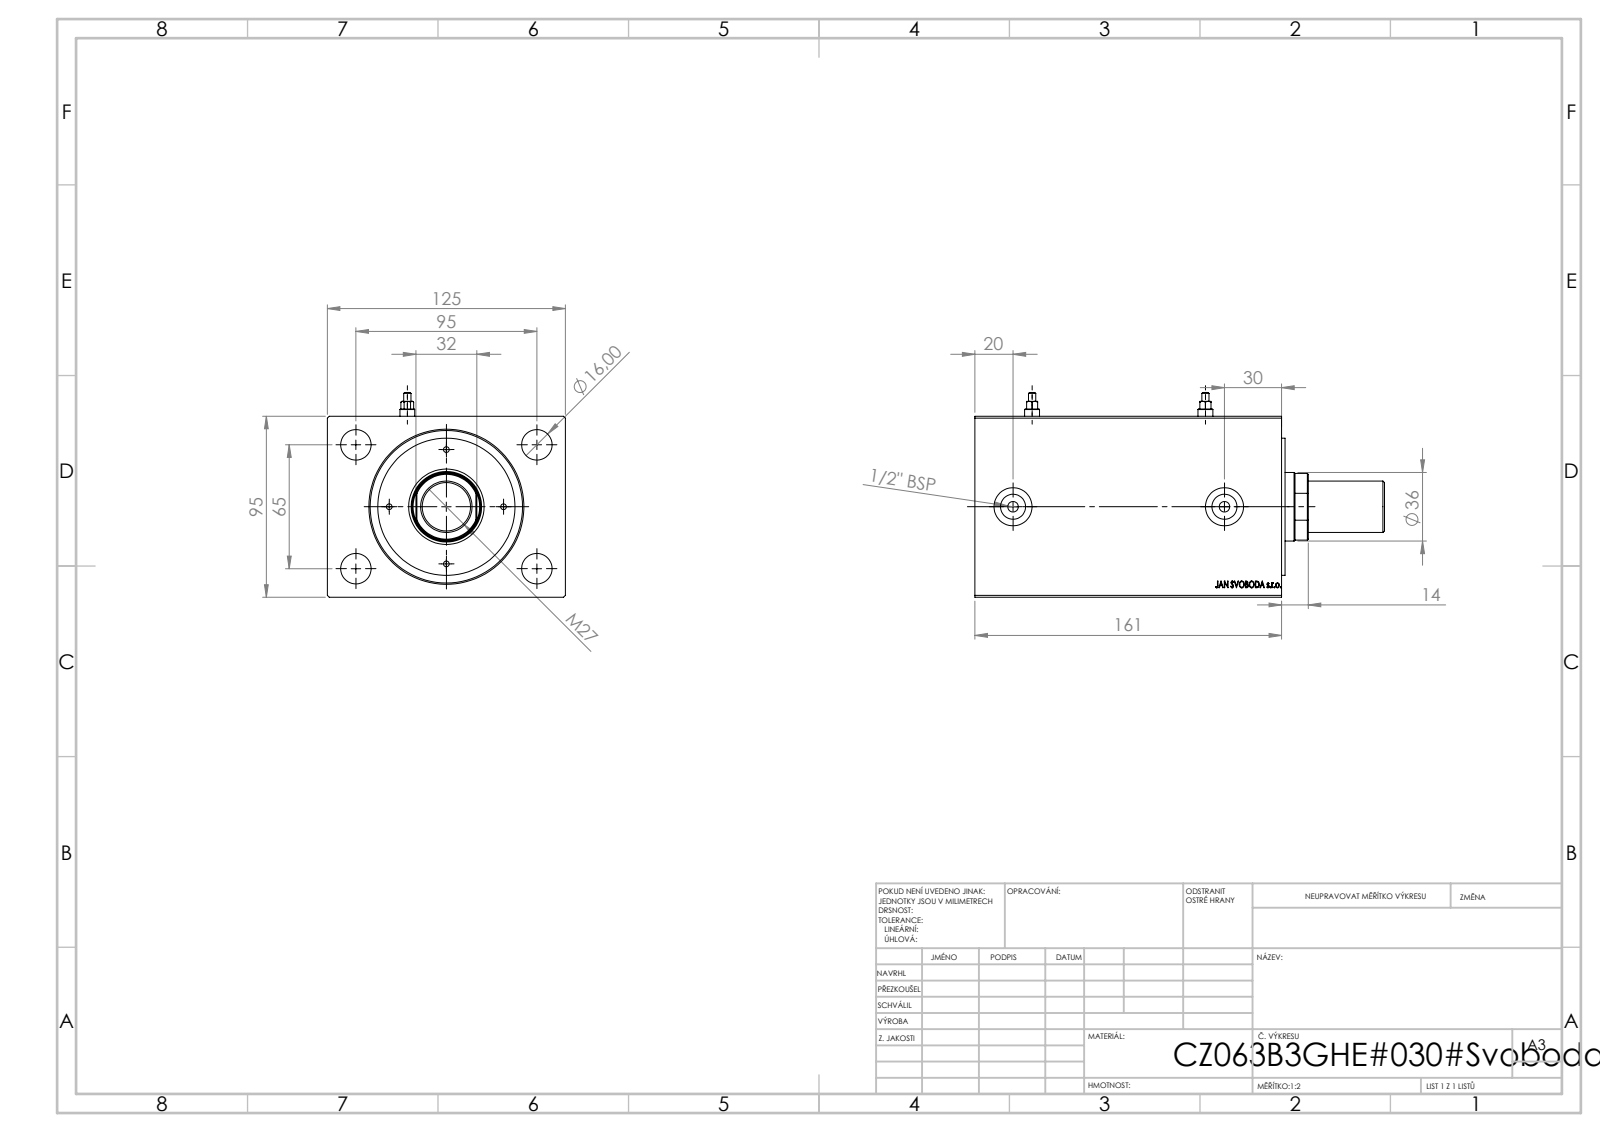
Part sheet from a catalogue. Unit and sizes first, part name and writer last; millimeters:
Units: millimetres
Overall size (bounding box): 215 × 125 × 107.5
Round holes (diameter × count): ⌀3 ×4, ⌀16 ×4, ⌀1.8 ×2, ⌀5.5 ×2, ⌀8 ×2, ⌀13.16 ×2, ⌀20 ×2, ⌀25.5 ×1, ⌀36 ×1, ⌀37 ×1, ⌀63 ×1, ⌀80 ×1
Round bosses / shafts (diameter × count): ⌀7.8 ×2, ⌀3.8 ×2, ⌀72 ×1, ⌀27 ×1
Partial cylindrical surfaces — rounded edges, fillets, slot ends (radius × count): R17.5 ×1
Main face-to-face distances: 95, 125, 161, 140.2, 20.8, 14, 12.2, 1.8, 128, 148.8
Hole centre spacings: 30, 36.91, 42.43, 47.57, 57.55, 78.5, 84.04, 60
Volume: 1 813 000 mm³ · Surface area: 187 755 mm²
Bodies: 6 solids, 940 faces (426 planar, 76 cylindrical, 438 other)
Part name (STEP PRODUCT): V500CZ_SMALL_MALE_METRIC; Zatka_Cushioning3; V500CZ; V500CZ_B_VC
STEP written by: SolidWorks 2019 (CONFIG_CONTROL_DESIGN)
